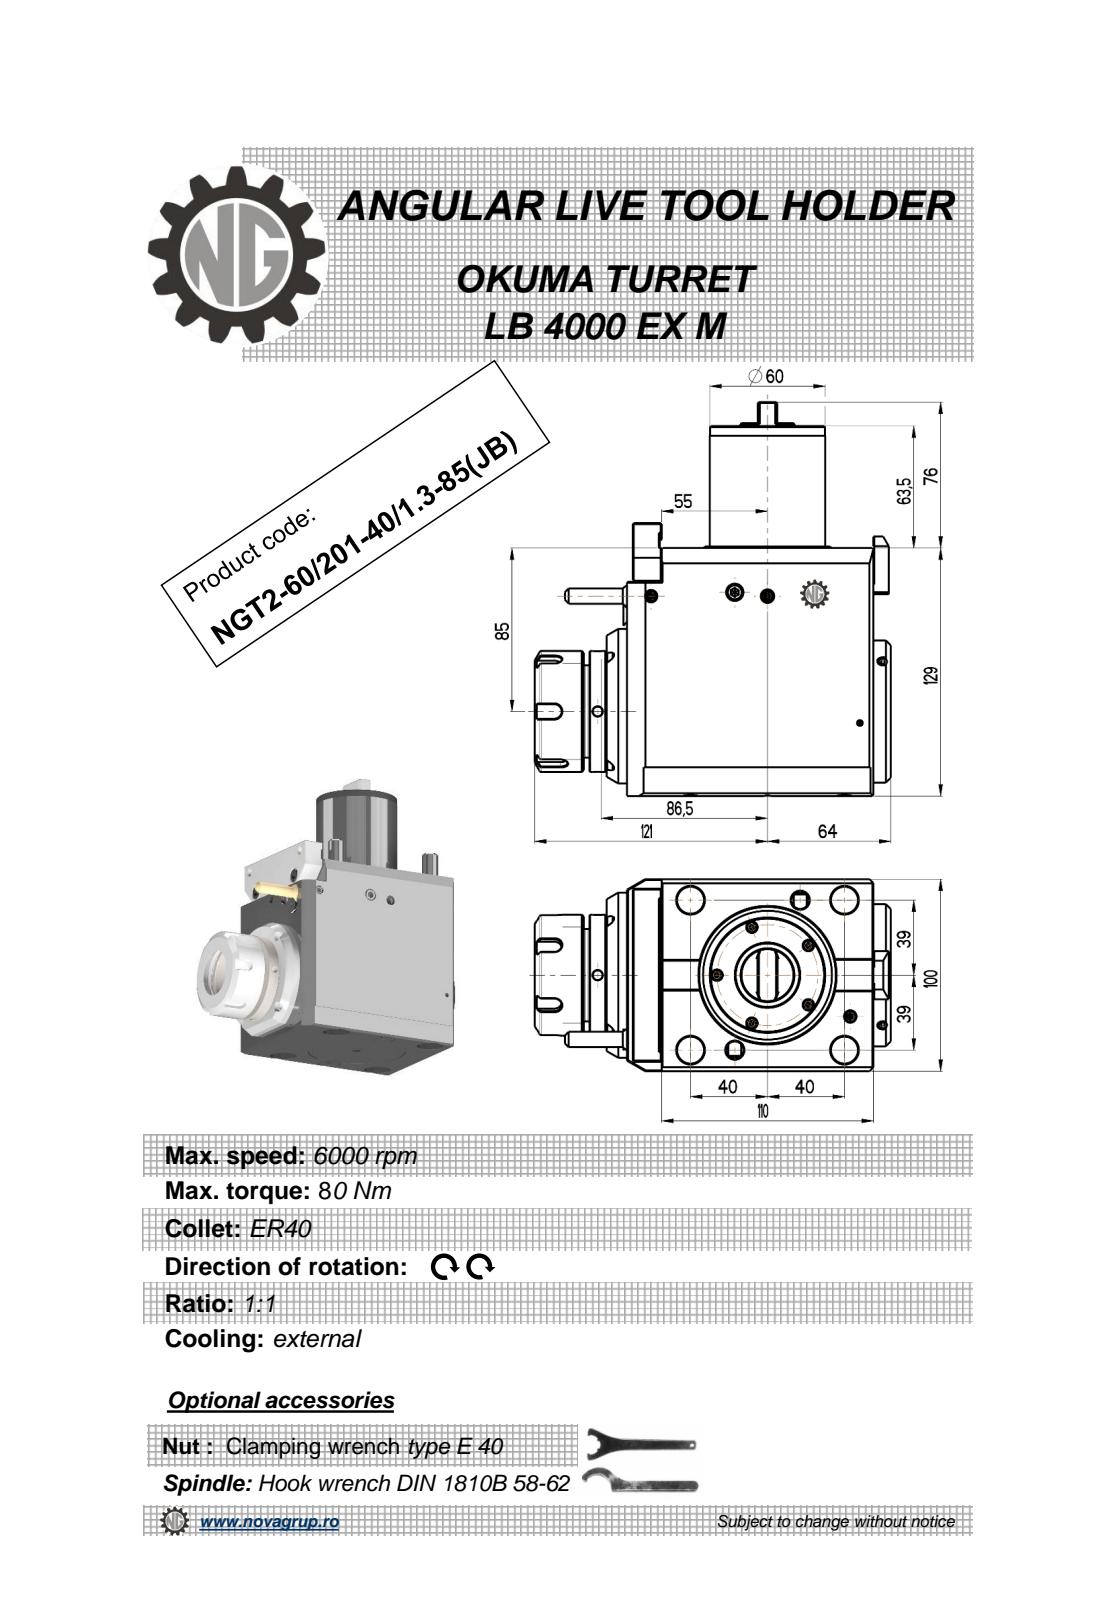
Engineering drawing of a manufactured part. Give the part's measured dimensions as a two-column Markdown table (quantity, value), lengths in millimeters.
| quantity | value |
| --- | --- |
| part name | NGT2_60_201_40_1_3_85_JB |
| STEP written by | PRO/ENGINEER BY PARAMETRIC TECHNOLOGY CORPORATION, 2010280 (CONFIG_CONTROL_DESIGN) |
| units | millimeters |
| bodies | 2 solids, 410 faces (196 planar, 97 cylindrical, 117 other) |
| overall size | 205 × 185 × 101.6 |
| volume | 2 039 000 mm³ |
| surface area | 127 562 mm² |
| round holes (diameter × count) | 5 × 5, 9 × 2, 3 × 1, 33.5 × 1, 71 × 1 |
| round bosses / shafts (diameter × count) | 14 × 4, 12 × 4, 6 × 3, 86 × 1, 74 × 1, 63 × 1, 60 × 1, 51 × 1 |
| partial cylindrical surfaces (radius × count) | 0.31 × 10, 0.22 × 6, 3.75 × 5, 0.8 × 2 |
| main face-to-face distances | 100, 129, 9, 128, 137, 147.5, 3, 138.5, 10.5, 0.5 |
| hole center spacings | 42.54, 99.16, 32.19, 68.72, 74, 77.42, 81.23, 85.09 |
